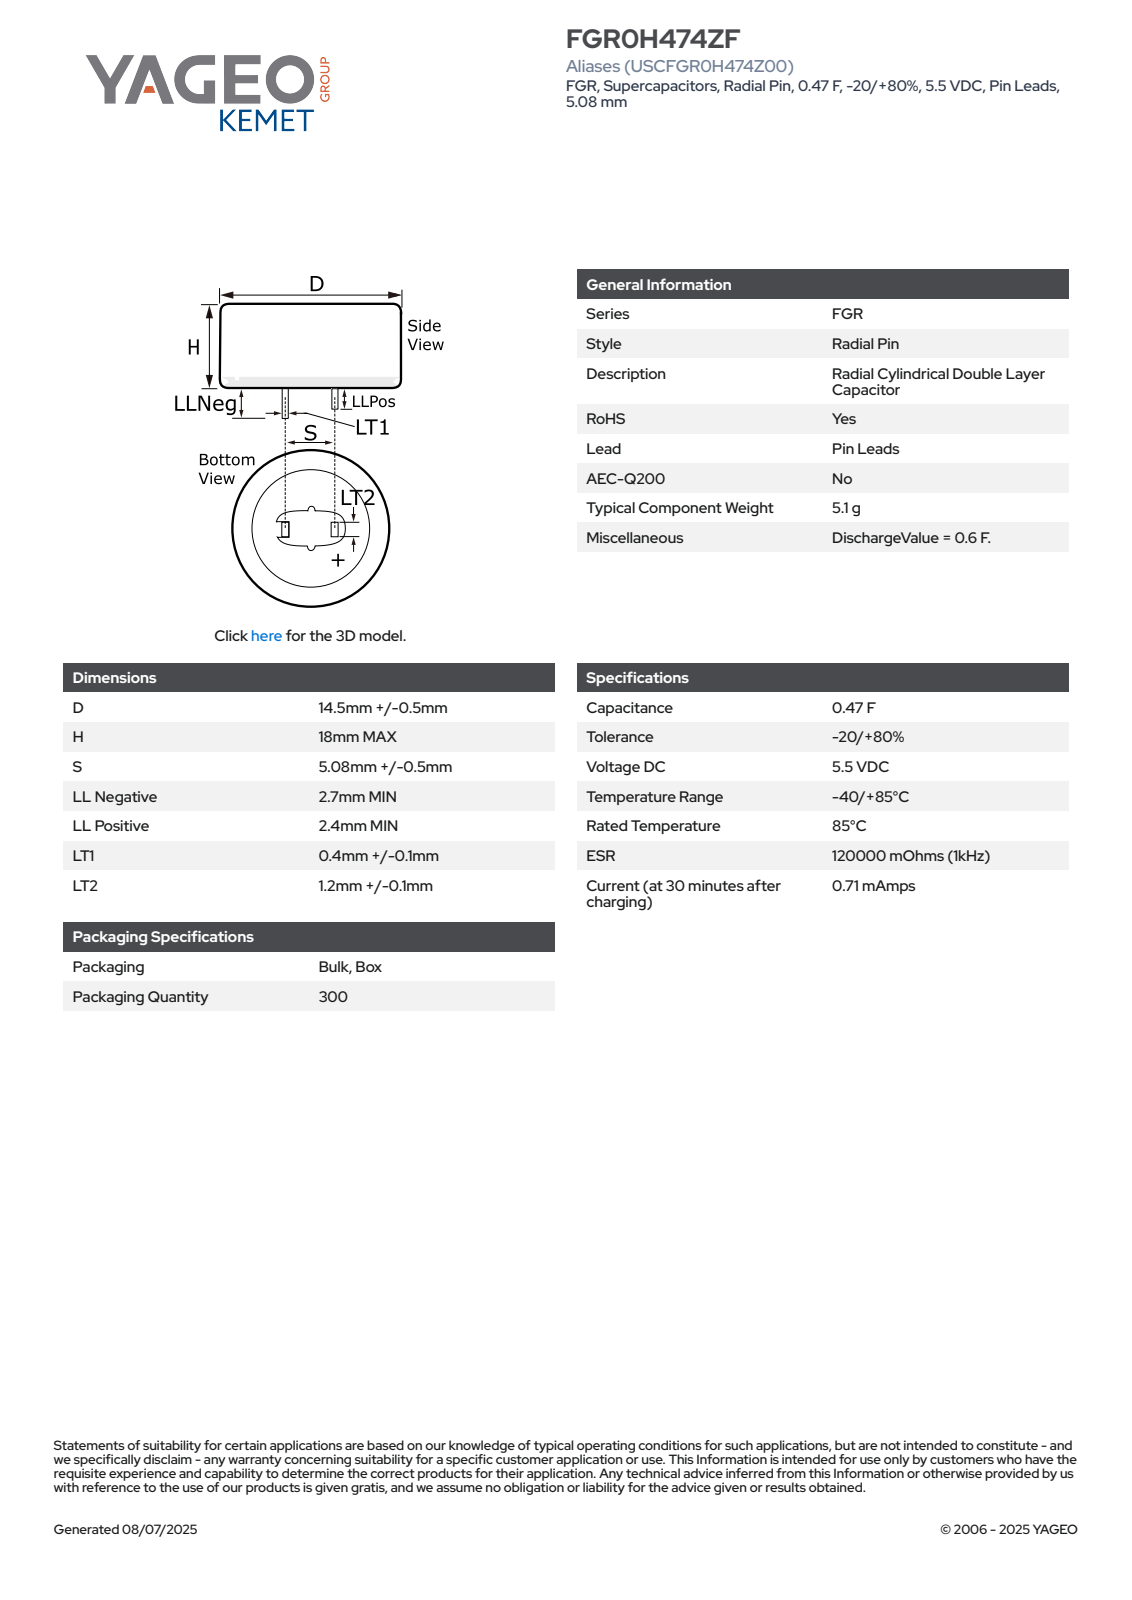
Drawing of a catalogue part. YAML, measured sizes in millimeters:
part_name: "CDR_LPLLN_D15L18S5.08LLNEG2.7LLPOS2.4LT10.5LT21.3"
step_written_by: "SolidWorks 2014 (AUTOMOTIVE_DESIGN)"
units: millimeters
bodies: {solids: 1, faces: 78, planar: 70, cylindrical: 4, other: 4}
overall_size: [20.7, 15, 15]
volume: 3158
surface_area: 1173
round_bosses_or_shafts:
  - {diameter: 15, count: 1}
partial_cylinders:
  - {radius: 7.51, count: 1}
face_to_face_distances: [18, 17.99, 0.5, 5.08, 5.58, 4.58, 1.3, 2.7, 20.69, 20.7]
